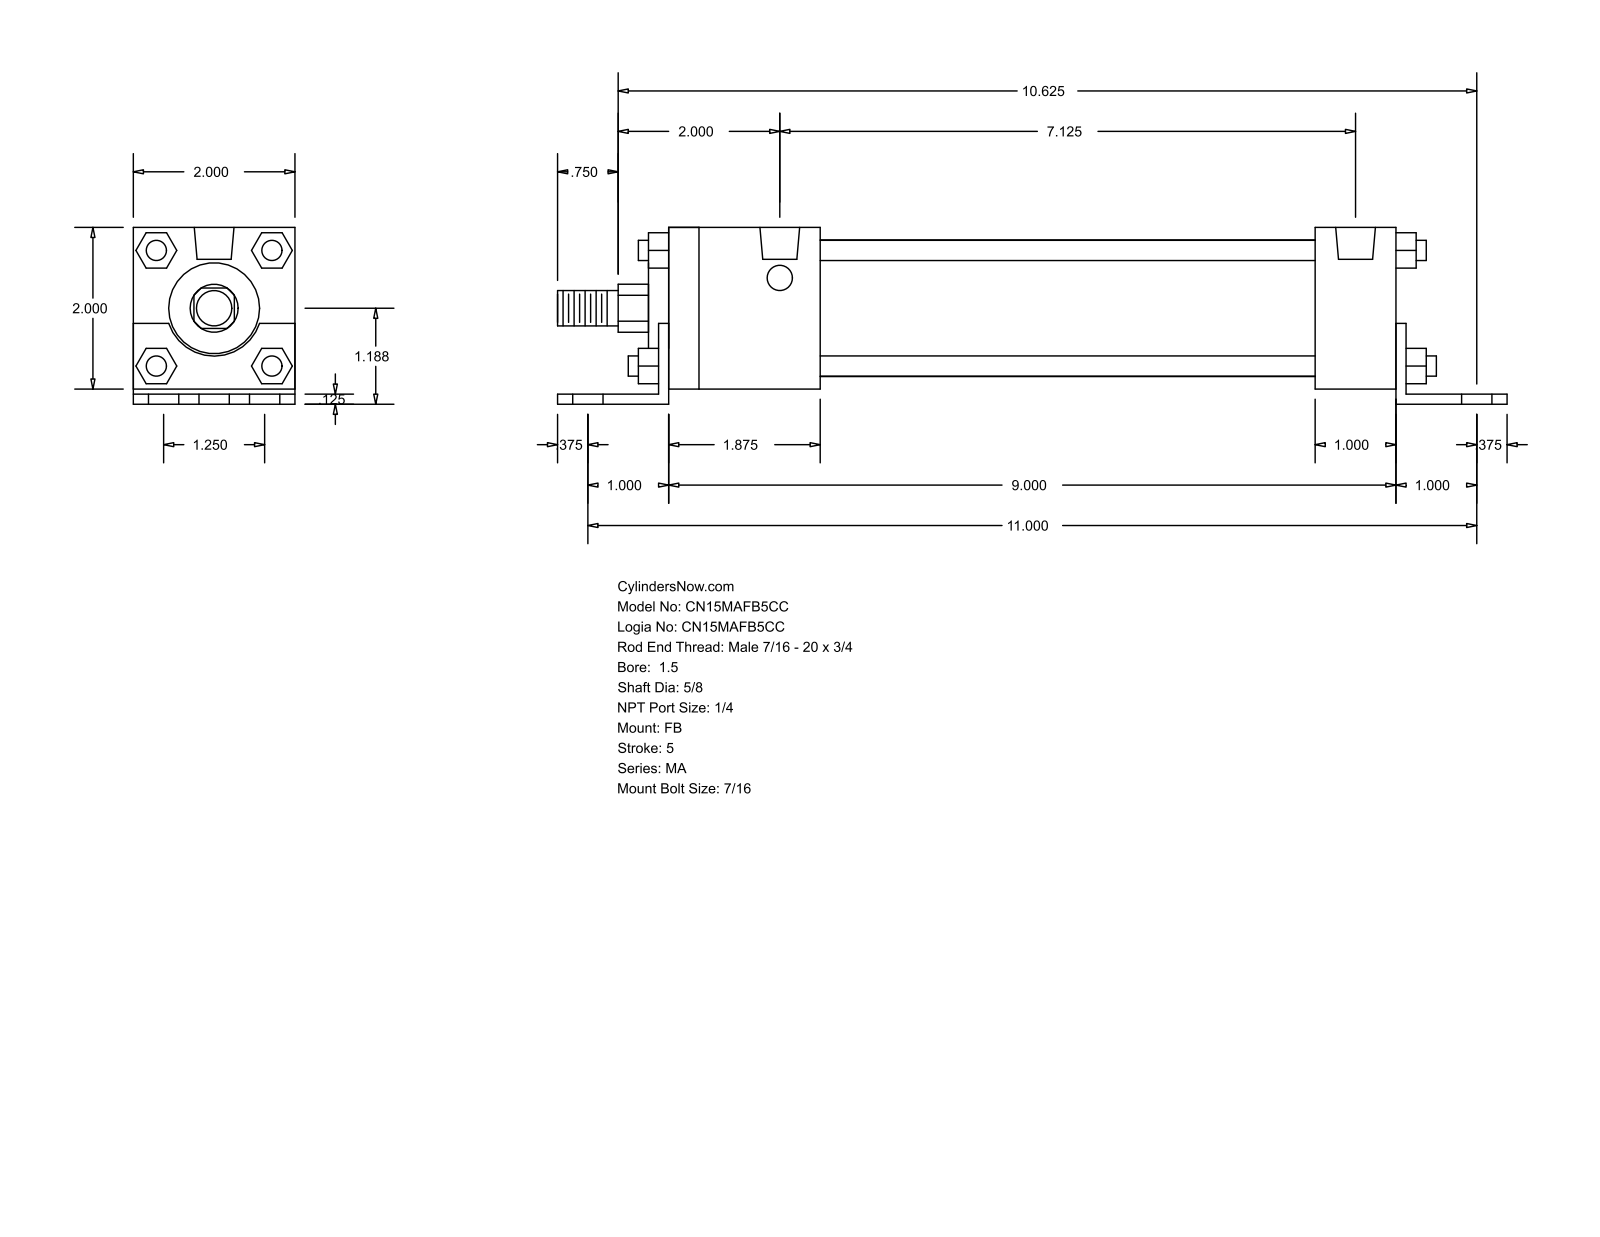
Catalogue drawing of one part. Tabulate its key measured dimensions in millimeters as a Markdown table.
| quantity | value |
| --- | --- |
| part name | MA_FB__0150_0.625 |
| STEP written by | GSSL Pune (CONFIG_CONTROL_DESIGN) |
| units | millimeters |
| bodies | 0 solids, 140 faces (105 planar, 35 cylindrical, 0 other) |
| overall size | 298.45 × 55.56 × 50.8 |
| round holes (diameter × count) | 11.11 × 6, 7.94 × 4, 12.49 × 2 |
| round bosses / shafts (diameter × count) | 6.35 × 4, 42.93 × 1, 28.57 × 1, 15.88 × 1, 11.11 × 1 |
| partial cylindrical surfaces (radius × count) | 7.54 × 1, 15.05 × 1 |
| main face-to-face distances | 50.8, 3.17, 4.76, 55.56, 1.59, 52.39, 3.18, 25.4, 231.77, 238.12 |
| hole center spacings | 15.88, 279.86, 279.41, 31.76, 41.28, 62.38, 180.98, 219.65 |
